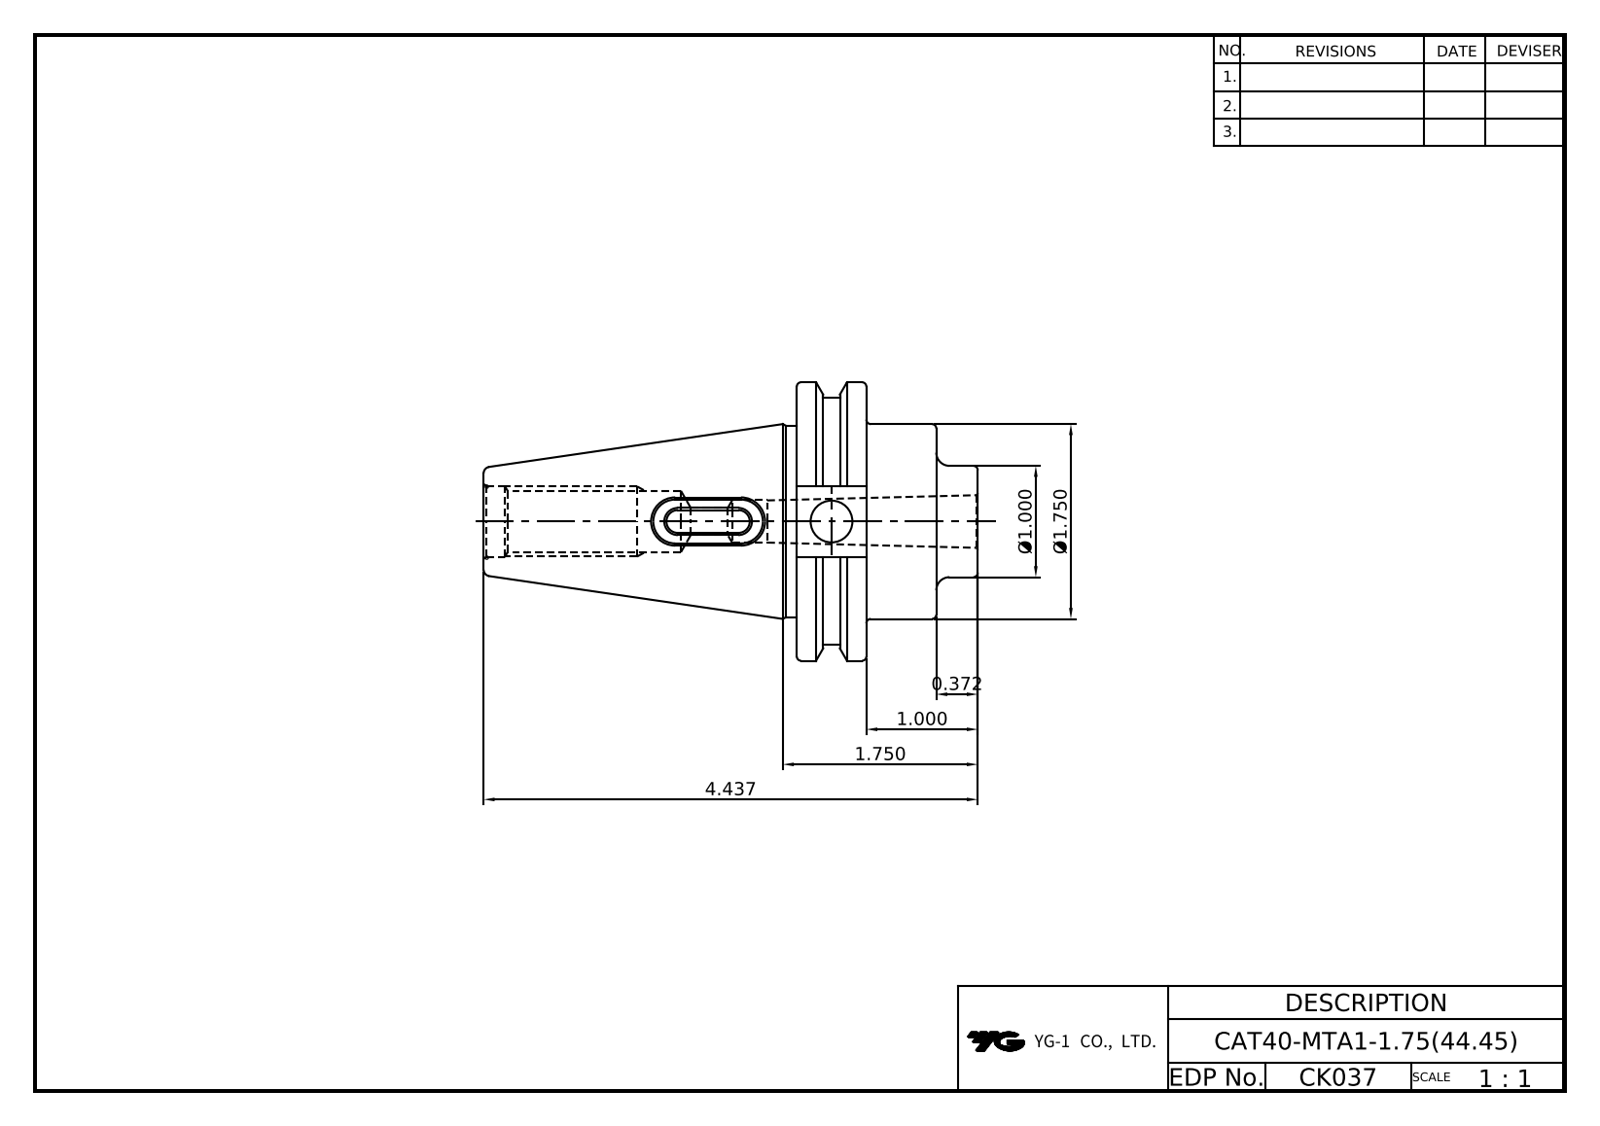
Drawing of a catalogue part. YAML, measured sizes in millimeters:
part_name: "LO-CAT40-MTA1-44.45"
step_written_by: "Autodesk Inventor 2025 (AUTOMOTIVE_DESIGN)"
units: millimeters
bodies: {solids: 1, faces: 101, planar: 40, cylindrical: 23, other: 38}
overall_size: [112.7, 63.5, 61.09]
volume: 126023
surface_area: 24442
round_holes:
  - {diameter: 9.53, count: 1}
  - {diameter: 9.7, count: 1}
  - {diameter: 13.39, count: 1}
  - {diameter: 16.3, count: 1}
round_bosses_or_shafts:
  - {diameter: 63.5, count: 1}
  - {diameter: 56.3, count: 1}
  - {diameter: 44.45, count: 1}
  - {diameter: 43.6, count: 1}
  - {diameter: 25.4, count: 1}
partial_cylinders:
  - {radius: 2.6, count: 2}
  - {radius: 5, count: 2}
  - {radius: 3.1, count: 1}
face_to_face_distances: [15.88, 31.83, 15.95, 2.4, 7.6, 3.19, 5.59, 10.79, 13.19, 41.28]
